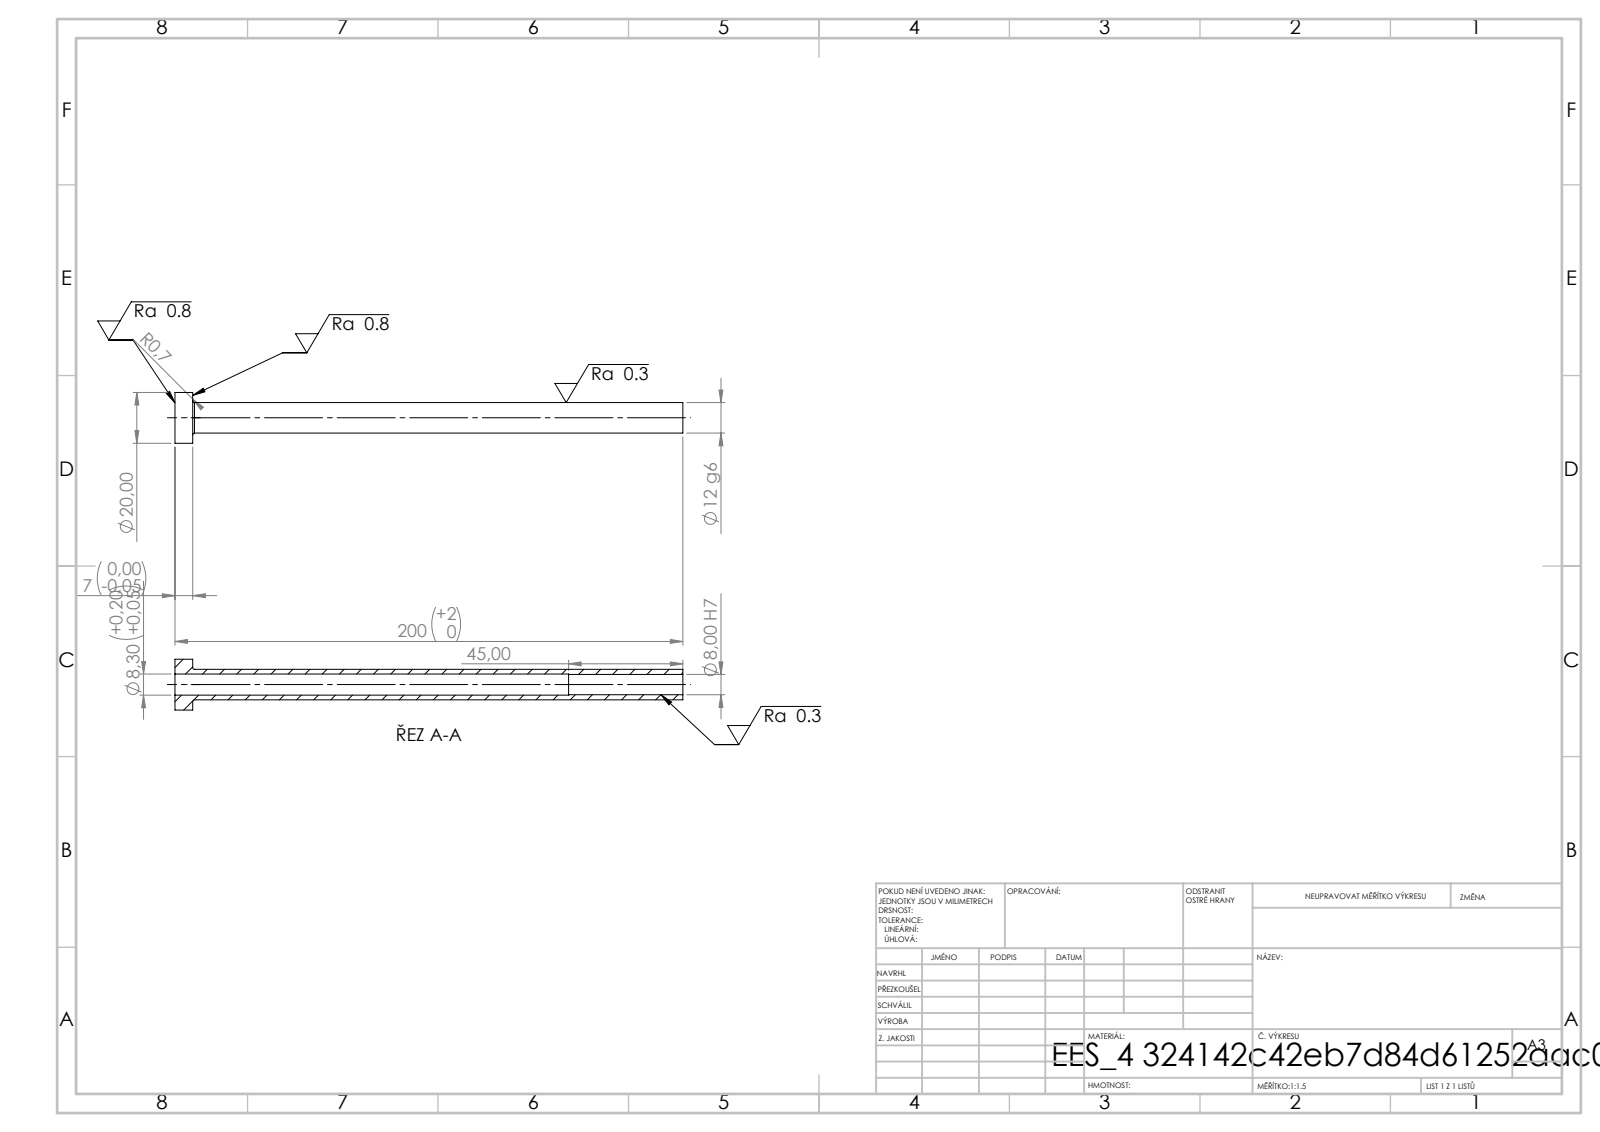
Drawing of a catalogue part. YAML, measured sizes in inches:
step_written_by: "SolidWorks 2019 (CONFIG_CONTROL_DESIGN)"
units: inches
bodies: {solids: 1, faces: 14, planar: 4, cylindrical: 8, other: 2}
overall_size: [7.874, 0.787, 0.787]
volume: 0.817
surface_area: 20.78
round_holes:
  - {diameter: 0.315, count: 1}
  - {diameter: 0.327, count: 1}
round_bosses_or_shafts:
  - {diameter: 0.787, count: 1}
  - {diameter: 0.472, count: 1}
face_to_face_distances: [0.276, 7.874, 7.598, 6.102, 5.827, 1.772]
